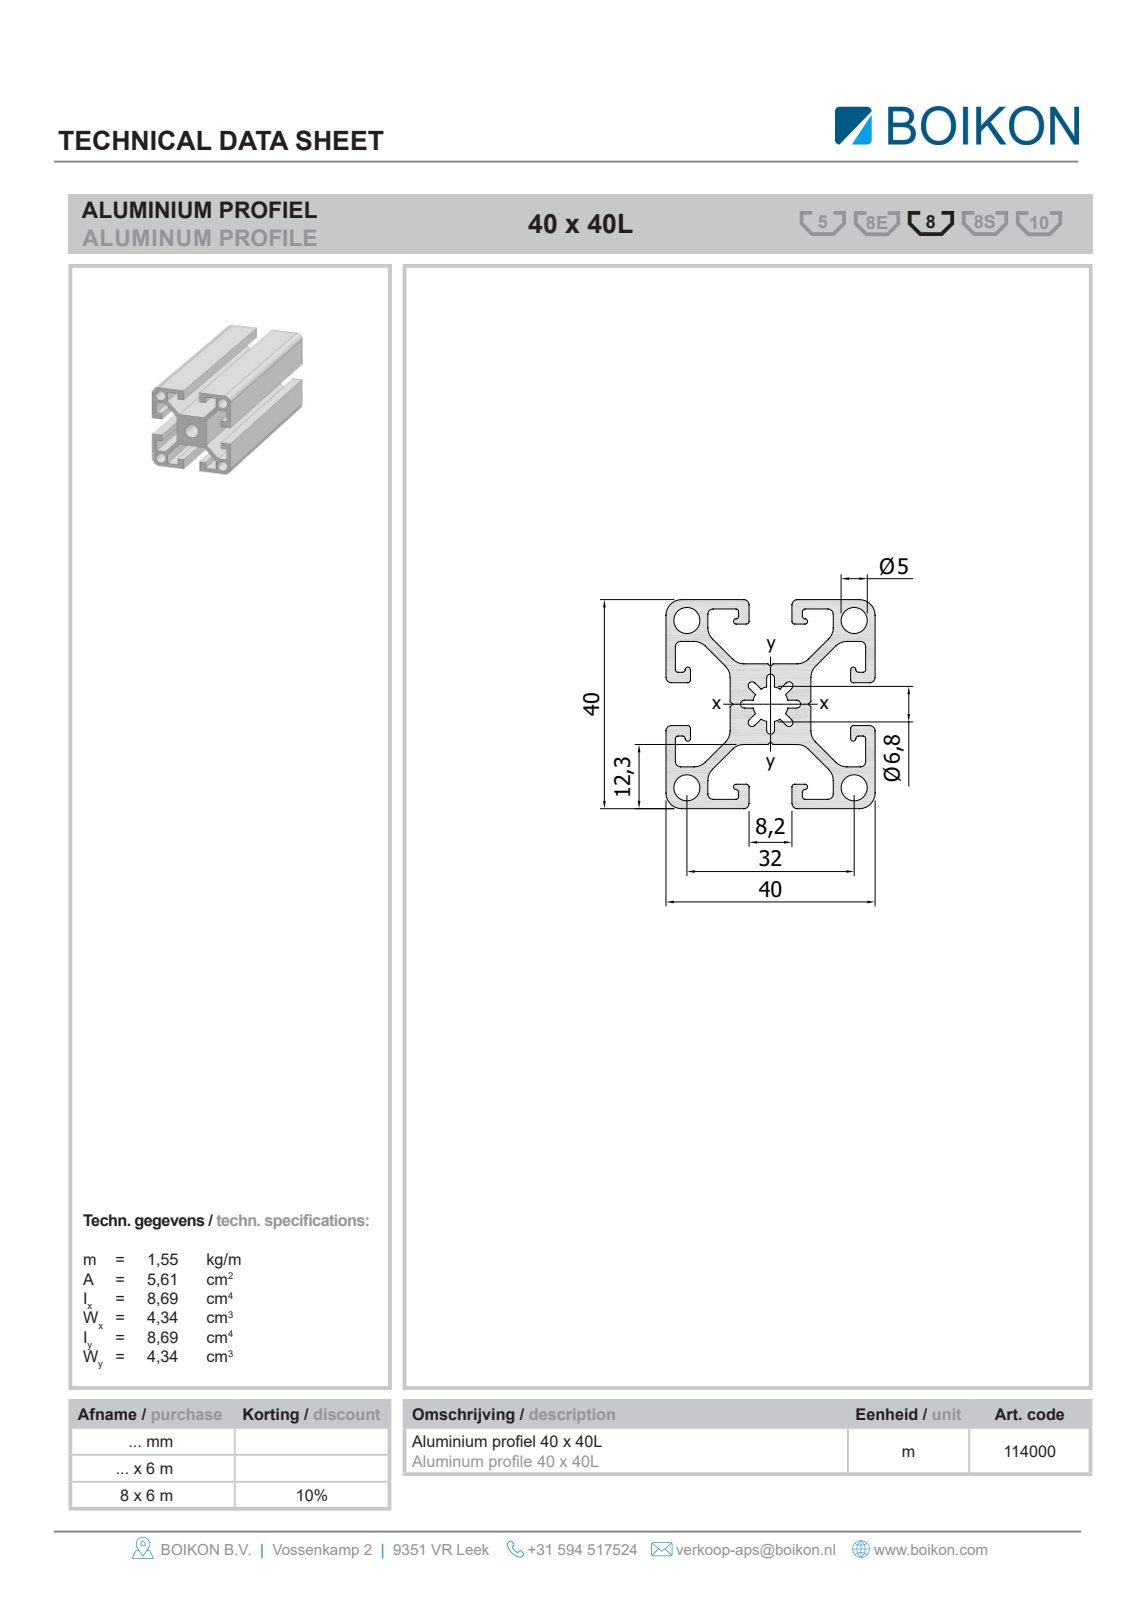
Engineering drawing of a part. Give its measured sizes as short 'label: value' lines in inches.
name: Root; 11400040x40LBOIKON0
written by: HiCAD 2013 1802.4 Build 509 (AUTOMOTIVE_DESIGN)
unit: in
bodies: 1 solid, 71 faces (62 planar, 9 cylindrical, 0 other)
size: 39.37 × 1.575 × 1.575
volume: 35.42 in³; area: 761.5 in²
holes: 4× ⌀0.197, 1× ⌀0.268
rounds: 4× R0.118
face distances: 0.071, 1.575, 0.488, 1.087, 0.441, 1.504, 0.417, 1.016, 0.323, 0.626
hole spacings: 0.891, 1.26, 1.781
